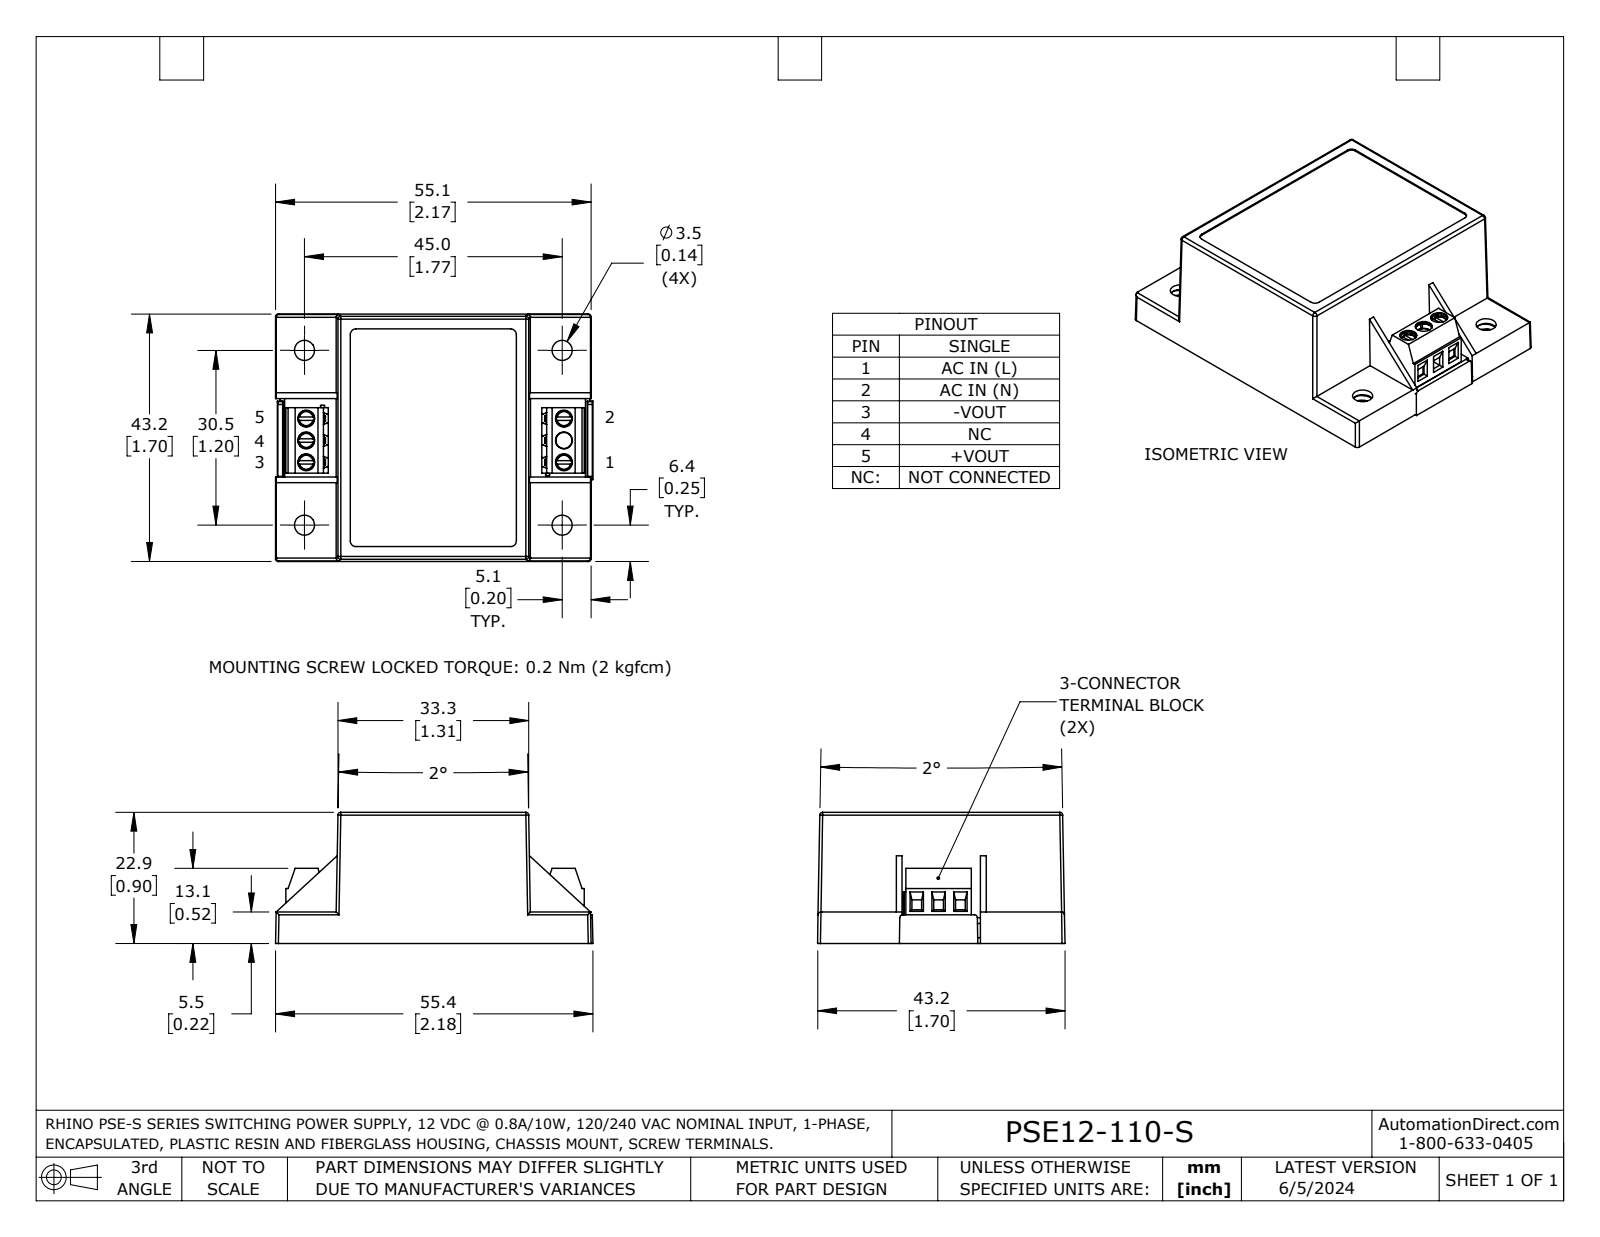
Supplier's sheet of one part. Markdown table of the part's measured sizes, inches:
| quantity | value |
| --- | --- |
| part name | PSE12-110-S |
| STEP written by | SolidWorks 2023 (AUTOMOTIVE_DESIGN) |
| units | inches |
| bodies | 5 solids, 655 faces (491 planar, 130 cylindrical, 34 other) |
| overall size | 2.005 × 1.708 × 1.701 |
| volume | 0.65 in³ |
| surface area | 34.63 in² |
| round holes (diameter × count) | 0.138 × 8, 0.116 × 6, 0.161 × 4, 0.11 × 1 |
| partial cylindrical surfaces (radius × count) | 0.02 × 19, 0.009 × 18, 0.006 × 12, 0.004 × 8, 0.008 × 4, 0.01 × 4, 0.039 × 4, 0.079 × 4 |
| main face-to-face distances | 0.039, 0.138, 0.854, 0.717, 0.177, 0.098, 0.815, 0.677, 0.894, 0.756 |
| hole center spacings | 1.772, 0.022, 0.15, 0.45, 0.6, 0.75, 1.201, 1.778 |
